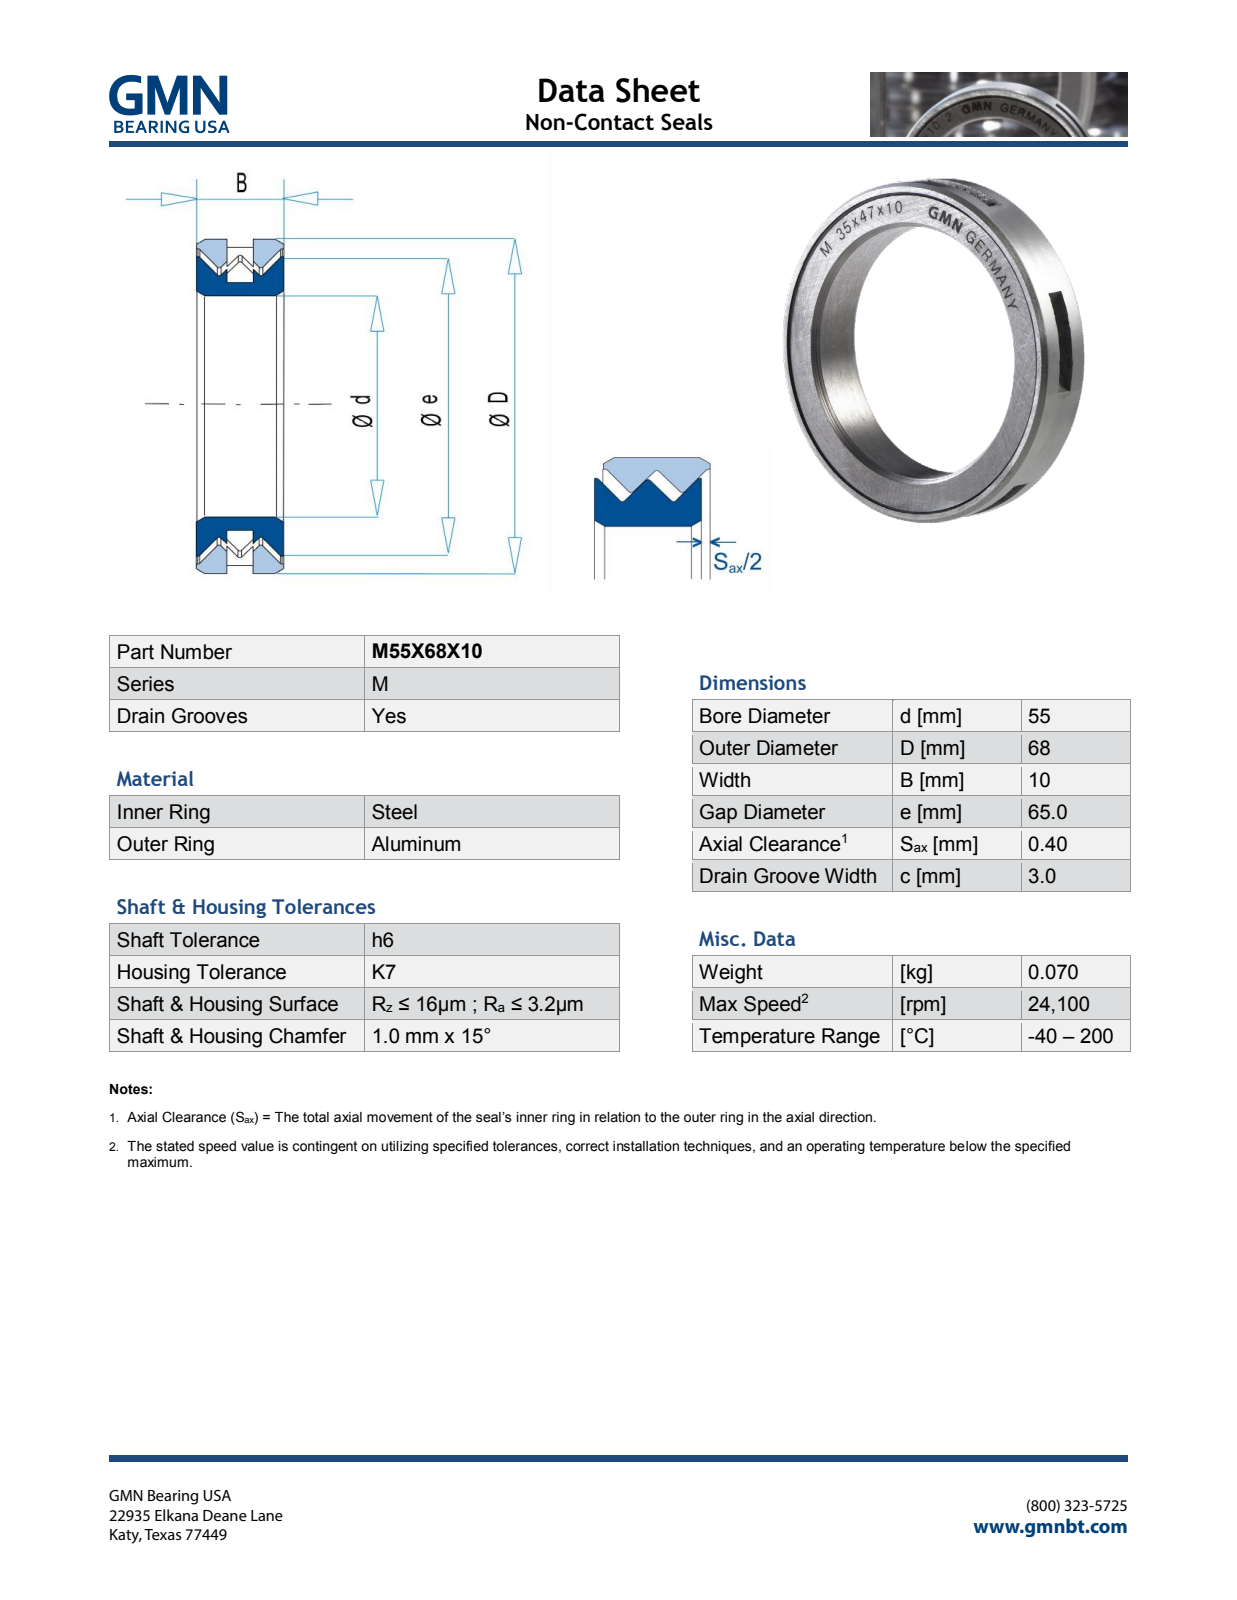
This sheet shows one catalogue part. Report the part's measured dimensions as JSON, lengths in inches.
{"part_name": "M55X68X10_PRT", "step_written_by": "PRO/ENGINEER BY PARAMETRIC TECHNOLOGY CORPORATION, 2013150 (AUTOMOTIVE_DESIGN)", "units": "inches", "bodies": {"solids": 2, "faces": 682, "planar": 605, "cylindrical": 27, "other": 50}, "overall_size": [2.677, 2.677, 0.396], "volume_in3": 0.681, "surface_area_in2": 17.61, "round_holes": [[2.165, 1], [2.57, 1]], "round_bosses_or_shafts": [[2.677, 1], [2.559, 1]], "partial_cylinders_radius": [[0.394, 5]], "face_to_face_distances": [0.394, 0.138, 0.256, 0.118, 0.141, 0.259, 0.396, 0.095, 0.012, 0.083]}
